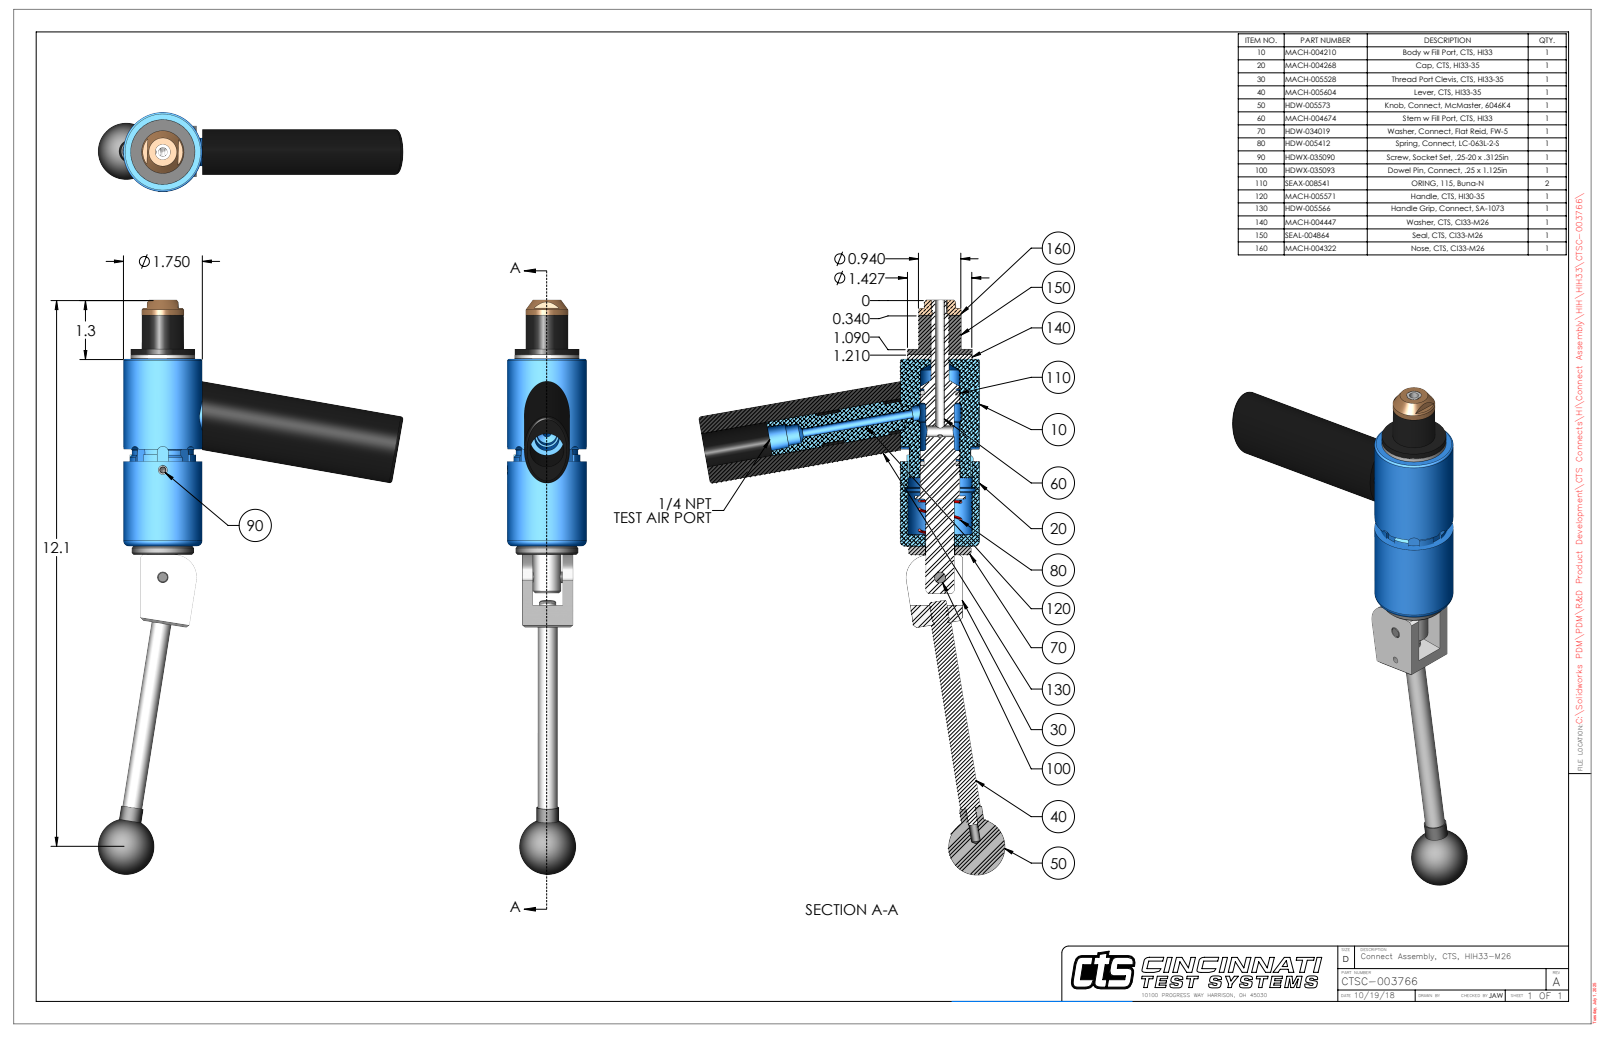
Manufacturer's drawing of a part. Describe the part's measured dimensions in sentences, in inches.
The part is named "CTSC-003766". Its 3-D file was written by "SolidWorks 2023 (AUTOMOTIVE_DESIGN)". It is 10 solids with 332 faces: 117 planar, 143 cylindrical and 72 other. Overall it measures 12.729 by 6.763 by 1.75 inches. Its volume is 18.3 cubic inches and its surface area 115 square inches. Round holes: 2 of diameter 0.201, 2 of diameter 0.313, 1 of diameter 0.15, 1 of diameter 0.187, 1 of diameter 0.204, 1 of diameter 0.249, 1 of diameter 0.25, 1 of diameter 0.251, 1 of diameter 0.39, 1 of diameter 0.397, 1 of diameter 0.398, 1 of diameter 0.438. Round bosses or shafts: 2 of diameter 0.375, 2 of diameter 0.312, 2 of diameter 0.25, 1 of diameter 1.75, 1 of diameter 1.427, 1 of diameter 1.38, 1 of diameter 0.94, 1 of diameter 0.75. Partial cylindrical surfaces (rounded edges, fillets, slot ends): 4 of radius 0.125, 2 of radius 0.029, 1 of radius 0.145, 1 of radius 0.166, 1 of radius 0.166, 1 of radius 0.33, 1 of radius 0.5, 1 of radius 0.695. The main face-to-face distances are 0.098, 4.244, 4.146, 1.12, 4.432, 4.334, 0.188, 0.232, 0.888, 0.232. The hole center spacings are 0.74, 2.376, 3.116.
